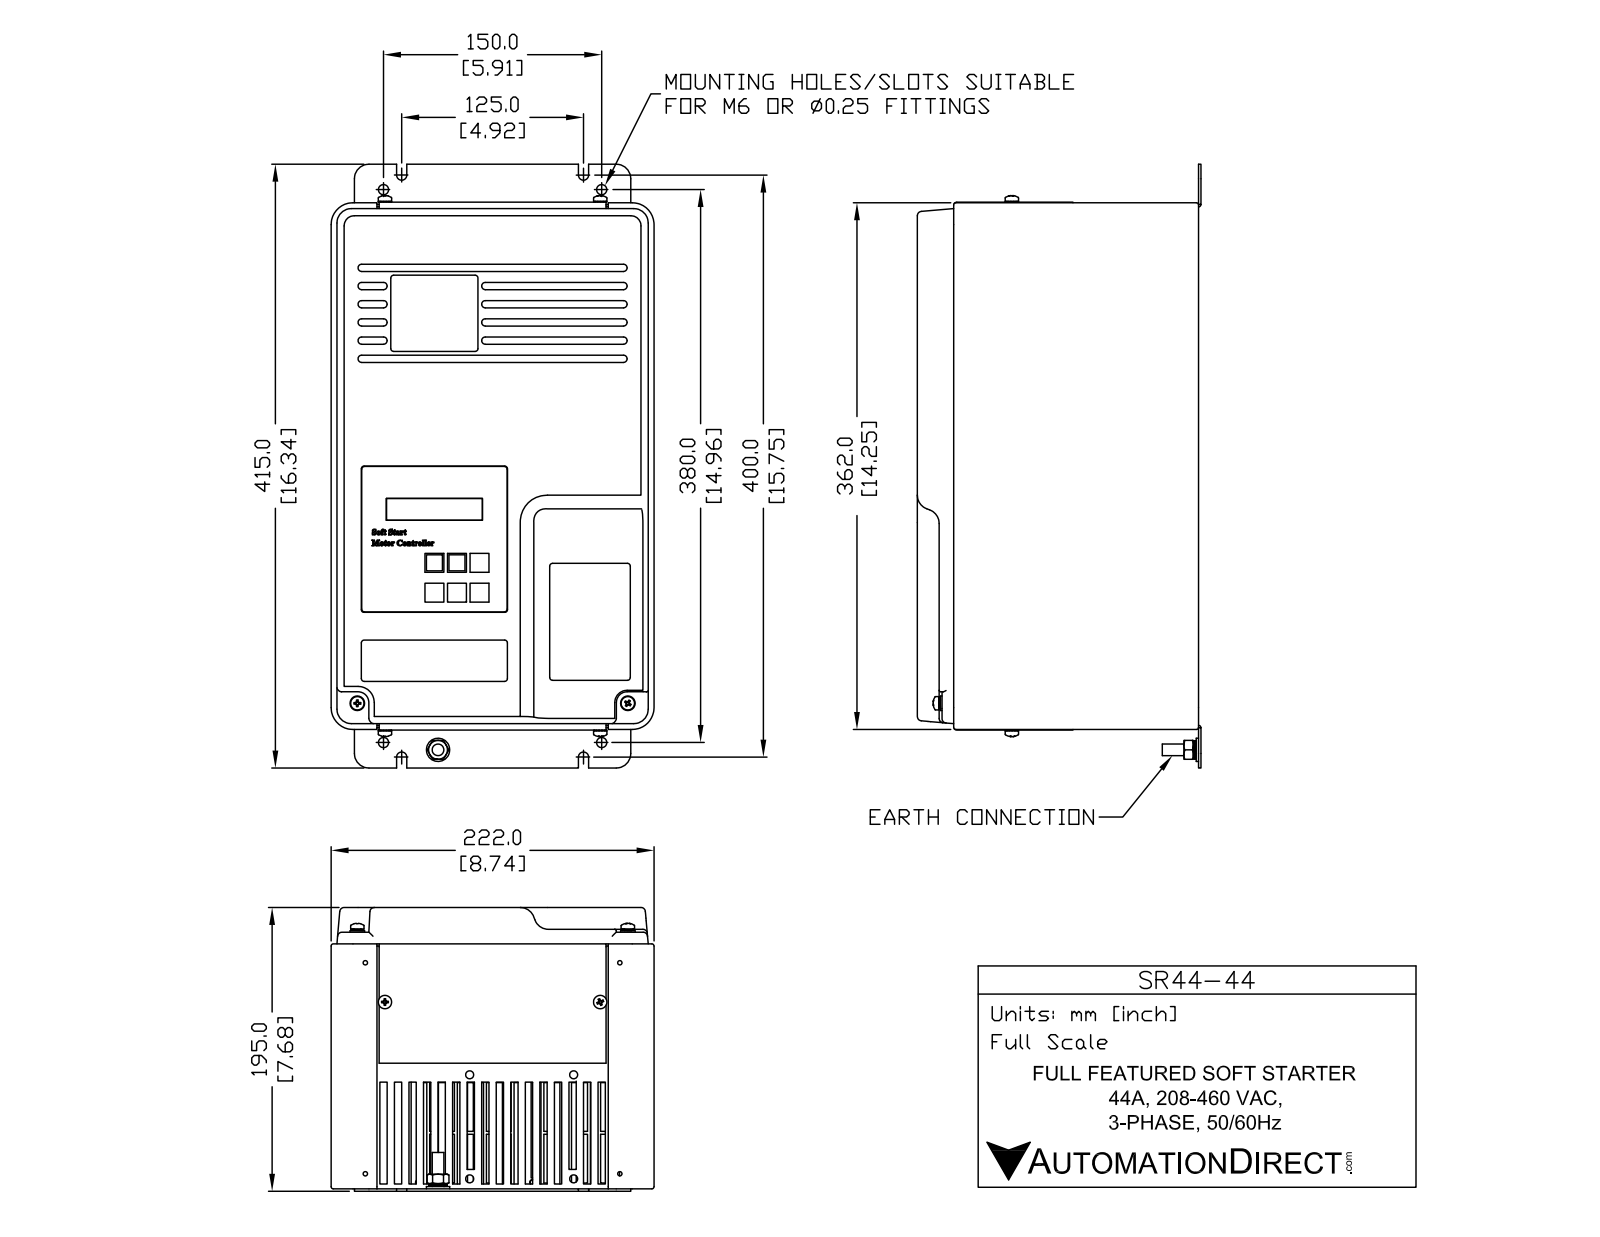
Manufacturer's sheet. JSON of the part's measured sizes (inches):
{"part_name": "SR44-44", "step_written_by": "SolidWorks 2013 (AUTOMOTIVE_DESIGN)", "units": "inches", "bodies": {"solids": 1, "faces": 768, "planar": 455, "cylindrical": 175, "other": 138}, "overall_size": [16.339, 8.74, 7.665], "volume_in3": 502.3, "surface_area_in2": 1102, "round_holes": [[0.276, 4]], "round_bosses_or_shafts": [[0.394, 4], [0.63, 1], [0.315, 1]], "partial_cylinders_radius": [[0.098, 30], [0.094, 28], [0.098, 12], [0.059, 11], [0.118, 8], [0.394, 8], [0.079, 6], [0.138, 4]], "face_to_face_distances": [0.401, 0.802, 1.204, 1.605, 2.006, 2.407, 2.808, 0.232, 3.209, 8.508], "hole_center_spacings": [5.906, 14.961, 16.084]}
